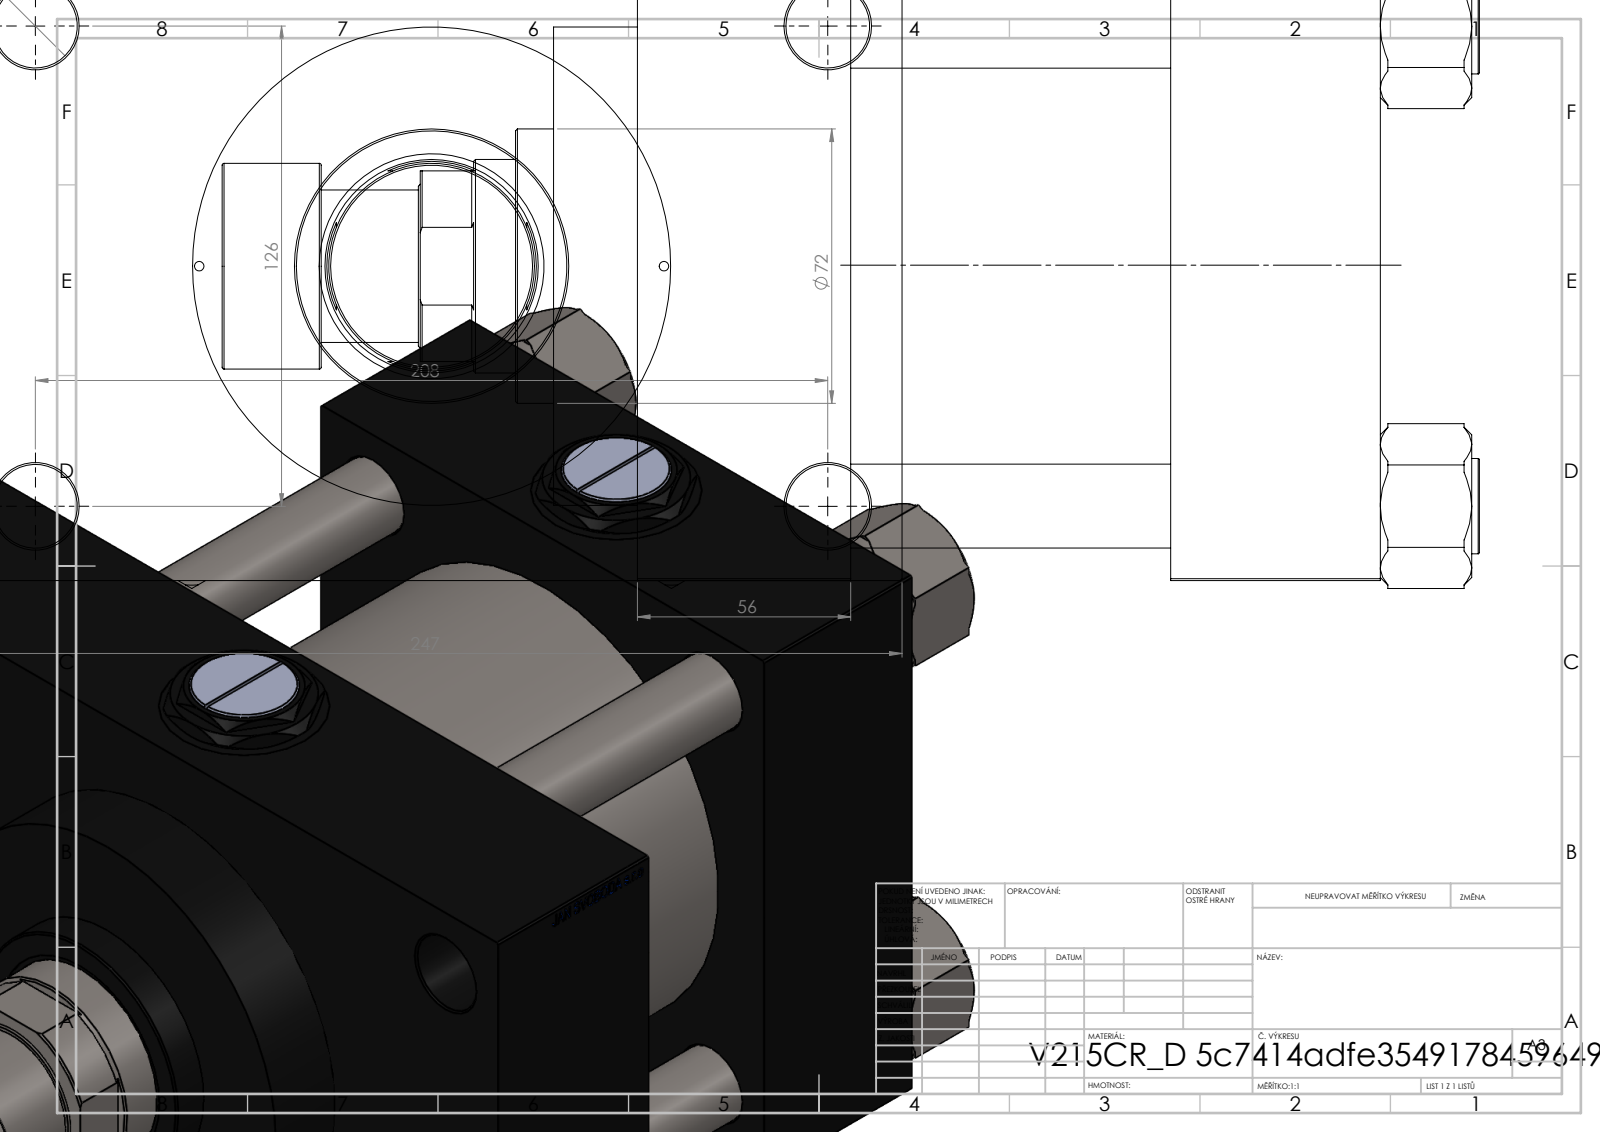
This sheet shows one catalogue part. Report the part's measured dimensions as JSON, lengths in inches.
{"part_name": "V215CR_VCP_D; Zatka_pro_OIL_PORT; V215_VC_A; NUT_M5_D (+3 more)", "step_written_by": "SolidWorks 2019 (CONFIG_CONTROL_DESIGN)", "units": "inches", "bodies": {"solids": 14, "faces": 1269, "planar": 598, "cylindrical": 105, "other": 566}, "overall_size": [12.992, 9.724, 6.853], "volume_in3": 304.8, "surface_area_in2": 863.3, "round_holes": [[0.866, 8], [1.269, 4], [1.772, 4], [0.276, 3], [0.098, 2], [1.594, 1], [2.205, 1], [2.323, 1], [3.78, 1], [4.921, 1], [4.941, 1]], "round_bosses_or_shafts": [[0.984, 4], [5.157, 1], [2.835, 1], [2.126, 1], [1.575, 1]], "face_to_face_distances": [6.496, 5.472, 3.307, 2.165, 2.205, 7.677, 5.512, 1.614, 8.11, 6.84], "hole_center_spacings": [1.616, 2.48, 3.003, 3.505, 4.787, 4.957, 5.215, 5.473]}
